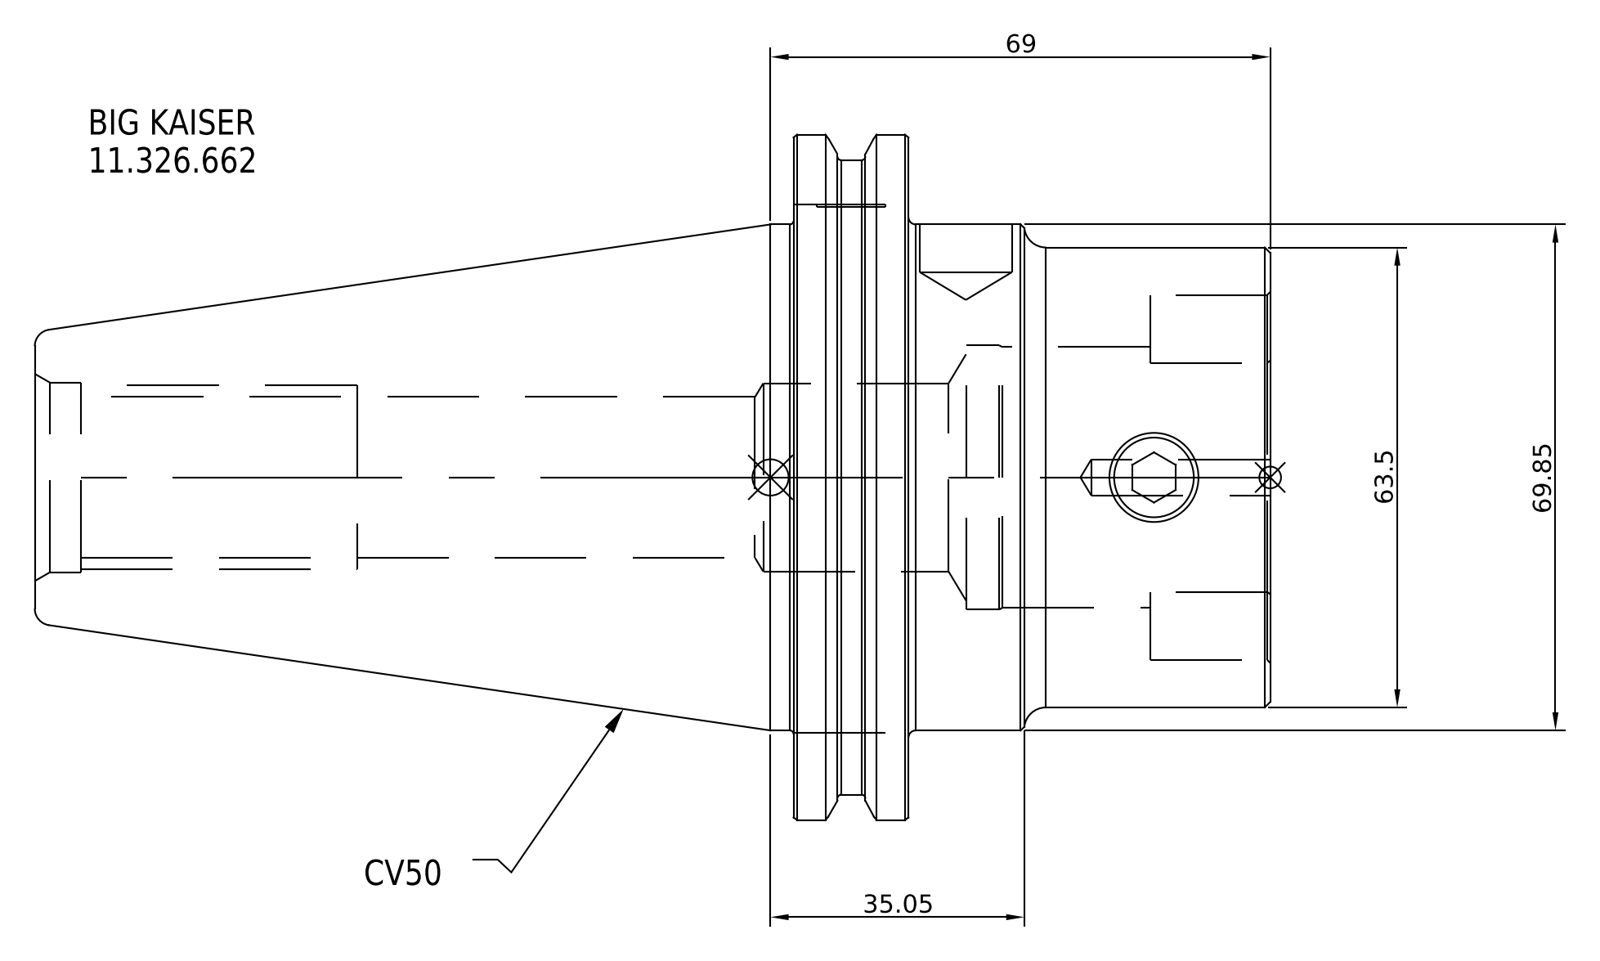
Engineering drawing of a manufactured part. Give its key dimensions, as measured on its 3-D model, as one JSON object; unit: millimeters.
{"part_name": "11.326.662", "step_written_by": "SolidWorks 2021 (CONFIG_CONTROL_DESIGN)", "units": "millimeters", "bodies": {"solids": 1, "faces": 16, "planar": 7, "cylindrical": 6, "other": 3}, "overall_size": [170.6, 98.43, 98.43], "volume_mm3": 549377, "surface_area_mm2": 47731, "round_bosses_or_shafts": [[98.43, 1], [91.29, 1], [69.85, 1], [63.27, 1]], "face_to_face_distances": [17.55, 49.95, 67.5, 170.6, 120.65, 103.1, 34, 15.95, 33.5, 136.6]}
